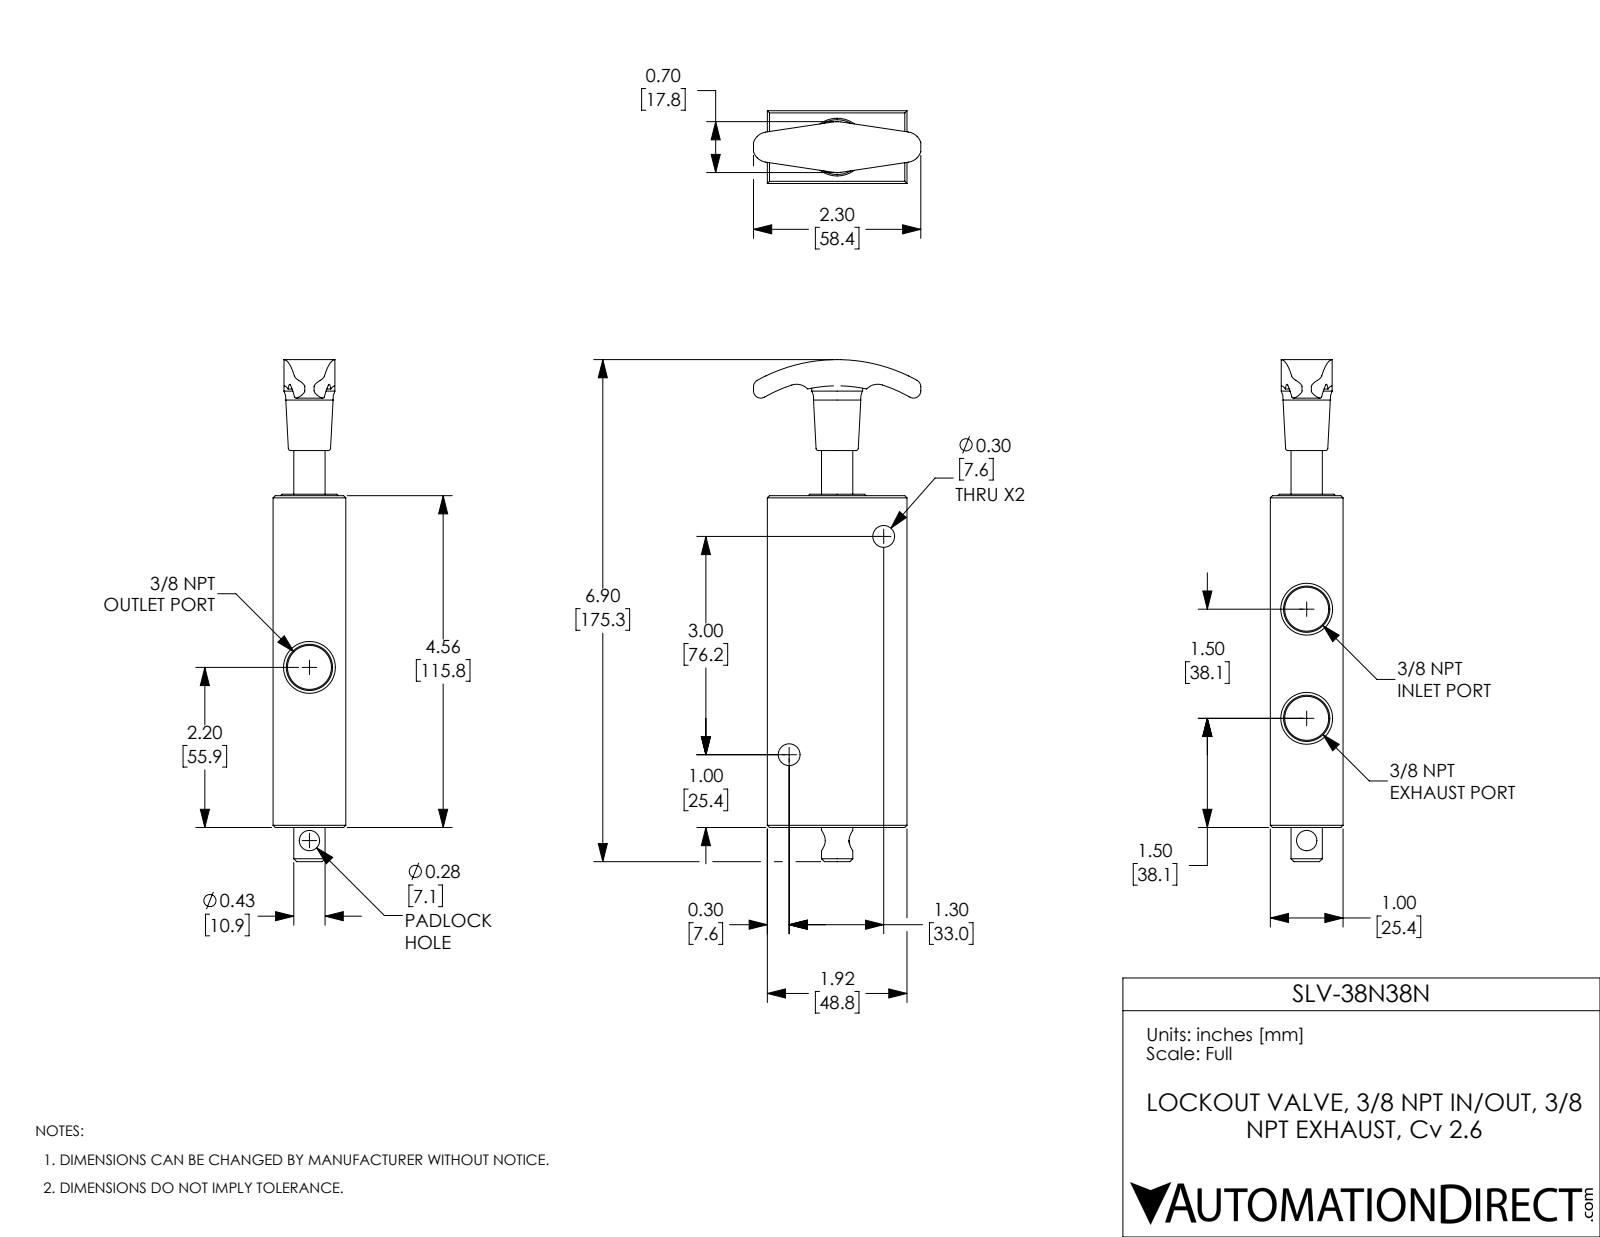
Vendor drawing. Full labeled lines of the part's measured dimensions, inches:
Part name (STEP PRODUCT): SLV-38N38N; SLV-38N38N_HANDLE; SLV-38N38N_BODY
STEP written by: SolidWorks 2017 (AUTOMOTIVE_DESIGN)
Units: inches
Bodies: 2 solids, 120 faces (27 planar, 51 cylindrical, 42 other)
Overall size (bounding box): 6.9 × 2.3 × 1
Volume: 8.783 in³ · Surface area: 55.5 in²
Round holes (diameter × count): ⌀0.104 ×4, ⌀0.605 ×3, ⌀0.3 ×2, ⌀0.28 ×1, ⌀0.45 ×1, ⌀0.79 ×1
Round bosses / shafts (diameter × count): ⌀0.7 ×1, ⌀0.43 ×1
Partial cylindrical surfaces — rounded edges, fillets, slot ends (radius × count): R0.1 ×4, R0.209 ×2, R0.21 ×2, R1.9 ×1, R2.01 ×1, R2.26 ×1
Main face-to-face distances: 1, 1.92, 4.56, 0.58, 1.34, 0.7, 0.76, 4.58, 0.02, 3.889
Hole centre spacings: 0.3, 0.424, 0.6, 0.7, 0.8, 1.5, 1.68, 2.38
